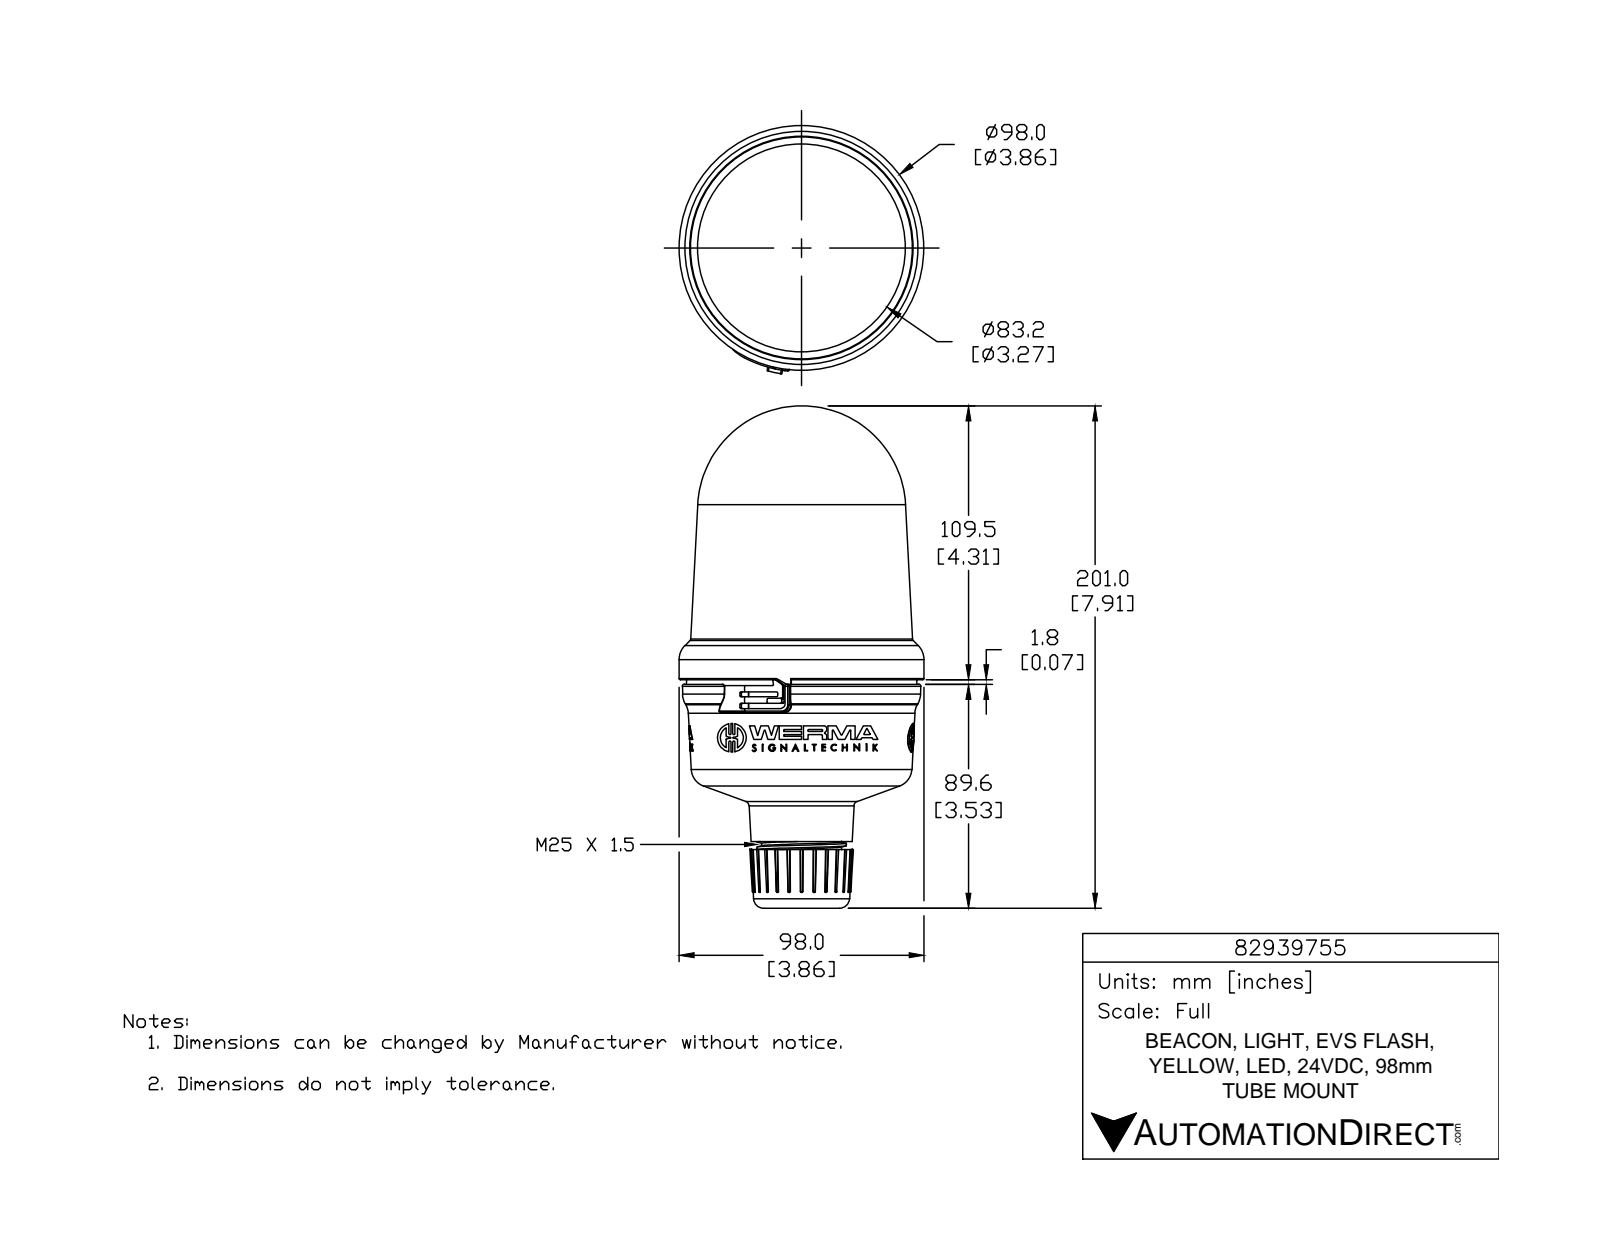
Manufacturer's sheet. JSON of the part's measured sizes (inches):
{"part_name": "82939755", "step_written_by": "SolidWorks 2015 (AUTOMOTIVE_DESIGN)", "units": "inches", "bodies": {"solids": 1, "faces": 1006, "planar": 554, "cylindrical": 189, "other": 263}, "overall_size": [7.914, 3.912, 3.858], "volume_in3": 54.7, "surface_area_in2": 91.39, "round_holes": [[0.078, 3], [1.013, 1], [1.024, 1]], "round_bosses_or_shafts": [[0.452, 3], [0.113, 3], [3.858, 1], [1.409, 1], [1.261, 1]], "partial_cylinders_radius": [[0.02, 12], [0.007, 9], [0.007, 6], [0.016, 6], [0.016, 6], [0.016, 6], [0.262, 6], [0.006, 3]], "face_to_face_distances": [2.214, 0.462, 2.676, 0.335, 0.127, 2.548, 2.603, 2.476, 2.141, 0.073]}
